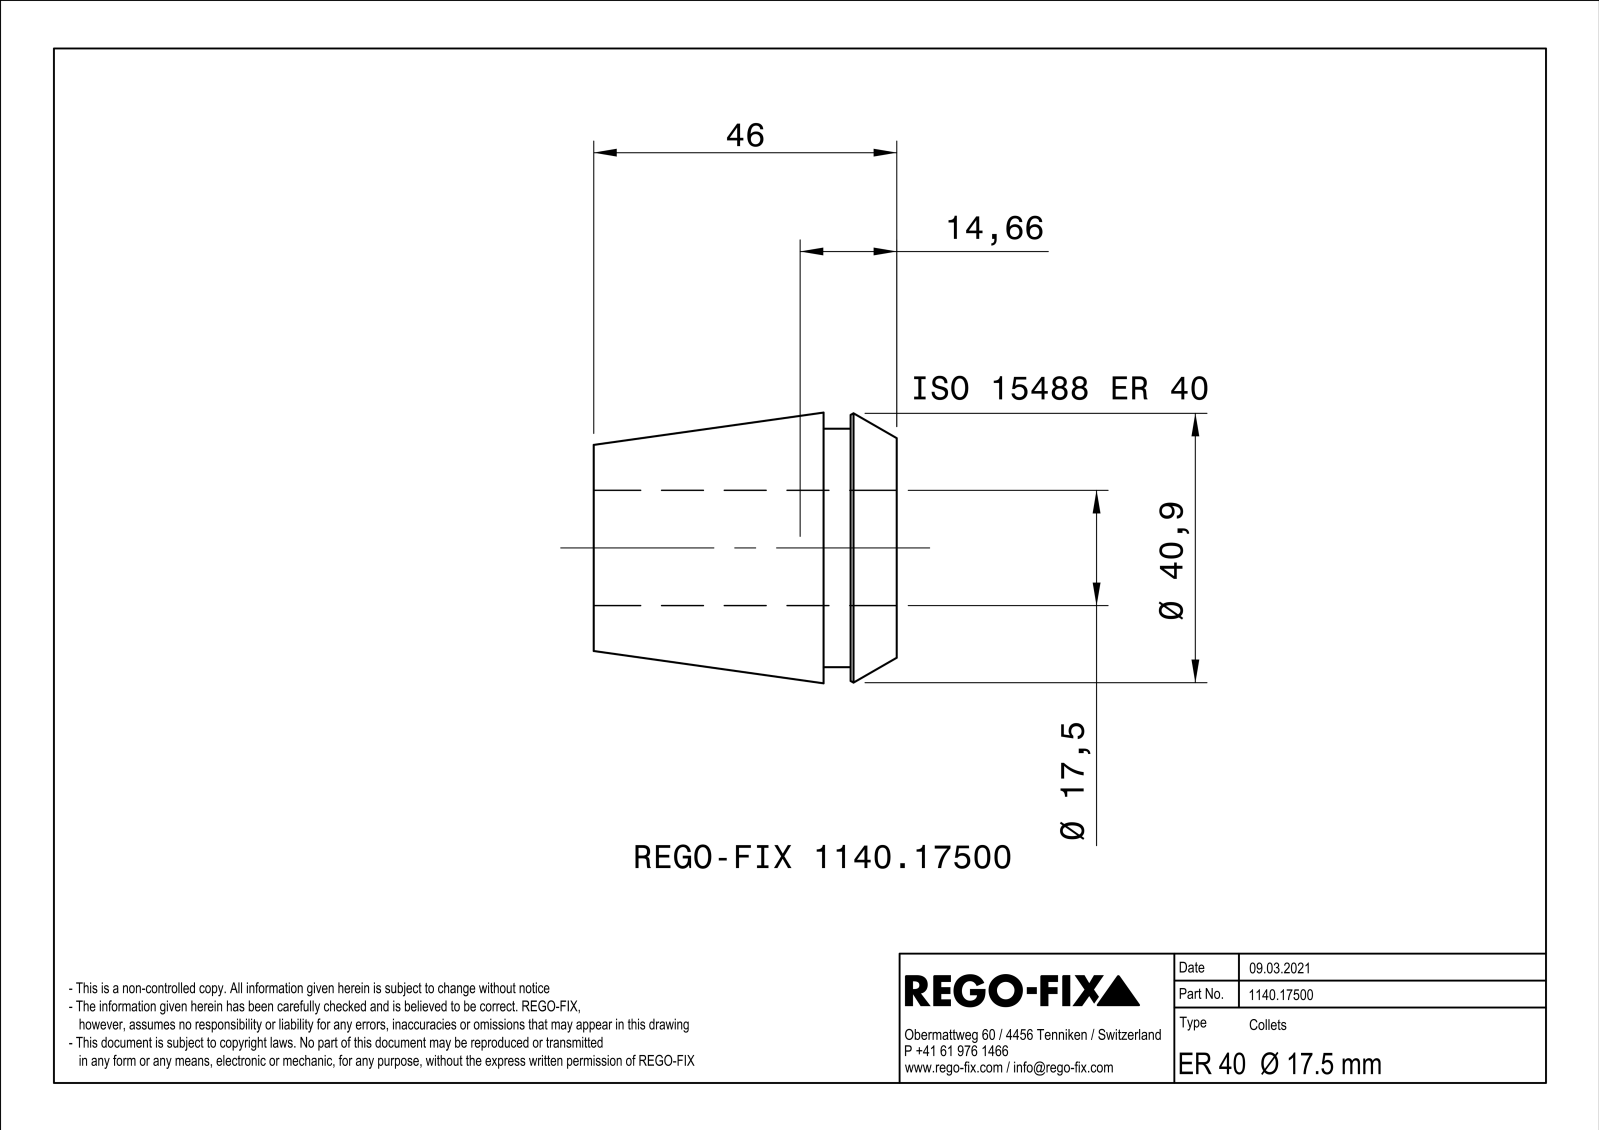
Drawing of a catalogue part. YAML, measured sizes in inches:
part_name: "NOCUT"
step_written_by: "SIEMENS PLM Software Solid Edge ST10 (AUTOMOTIVE_DESIGN)"
units: inches
bodies: {solids: 1, faces: 177, planar: 88, cylindrical: 9, other: 80}
overall_size: [1.811, 1.614, 1.614]
volume: 1.87
surface_area: 31.77
round_holes:
  - {diameter: 0.689, count: 1}
round_bosses_or_shafts:
  - {diameter: 1.425, count: 1}
face_to_face_distances: [0.039, 1.811, 0.437, 1.374, 0.276, 0.161, 1.535, 0.295, 0.02, 0.142]
